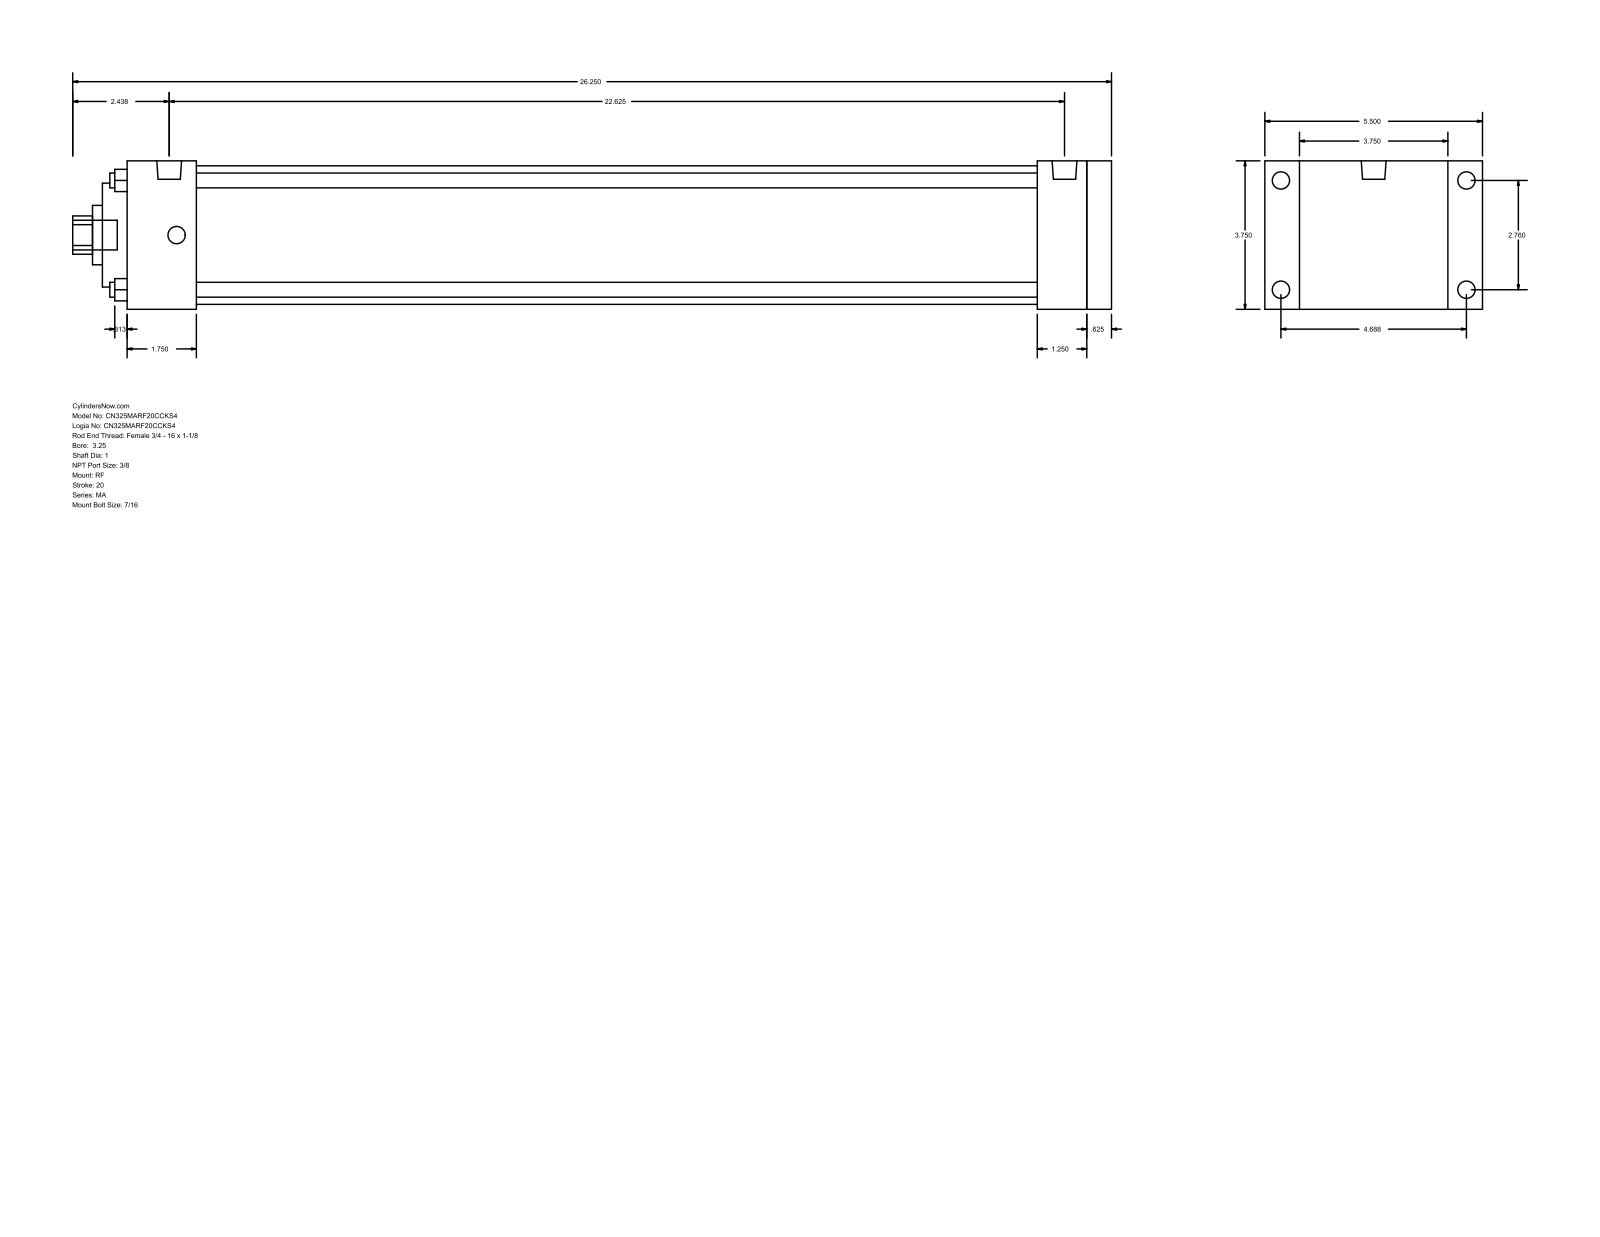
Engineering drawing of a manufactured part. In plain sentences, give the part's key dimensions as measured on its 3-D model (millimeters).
The part is named "MA_RF__0325_1". Its 3-D file was written by "GSSL Pune (CONFIG_CONTROL_DESIGN)". It is 0 solids with 94 faces: 65 planar, 29 cylindrical and 0 other. Overall it measures 666.75 by 139.7 by 95.25 millimeters. Round holes: 4 of diameter 9.53, 1 of diameter 25.4, 1 of diameter 38.1, 1 of diameter 66.67, 1 of diameter 88.9. Round bosses or shafts: 8 of diameter 11.11, 2 of diameter 15.93, 1 of diameter 19.05. Partial cylindrical surfaces (rounded edges, fillets, slot ends): 1 of radius 12.29. The main face-to-face distances are 95.24, 631.83, 15.87, 615.96, 22.23, 117.47, 584.2, 31.76, 47.63, 44.46. The hole center spacings are 49.57, 70.1, 99.14.
